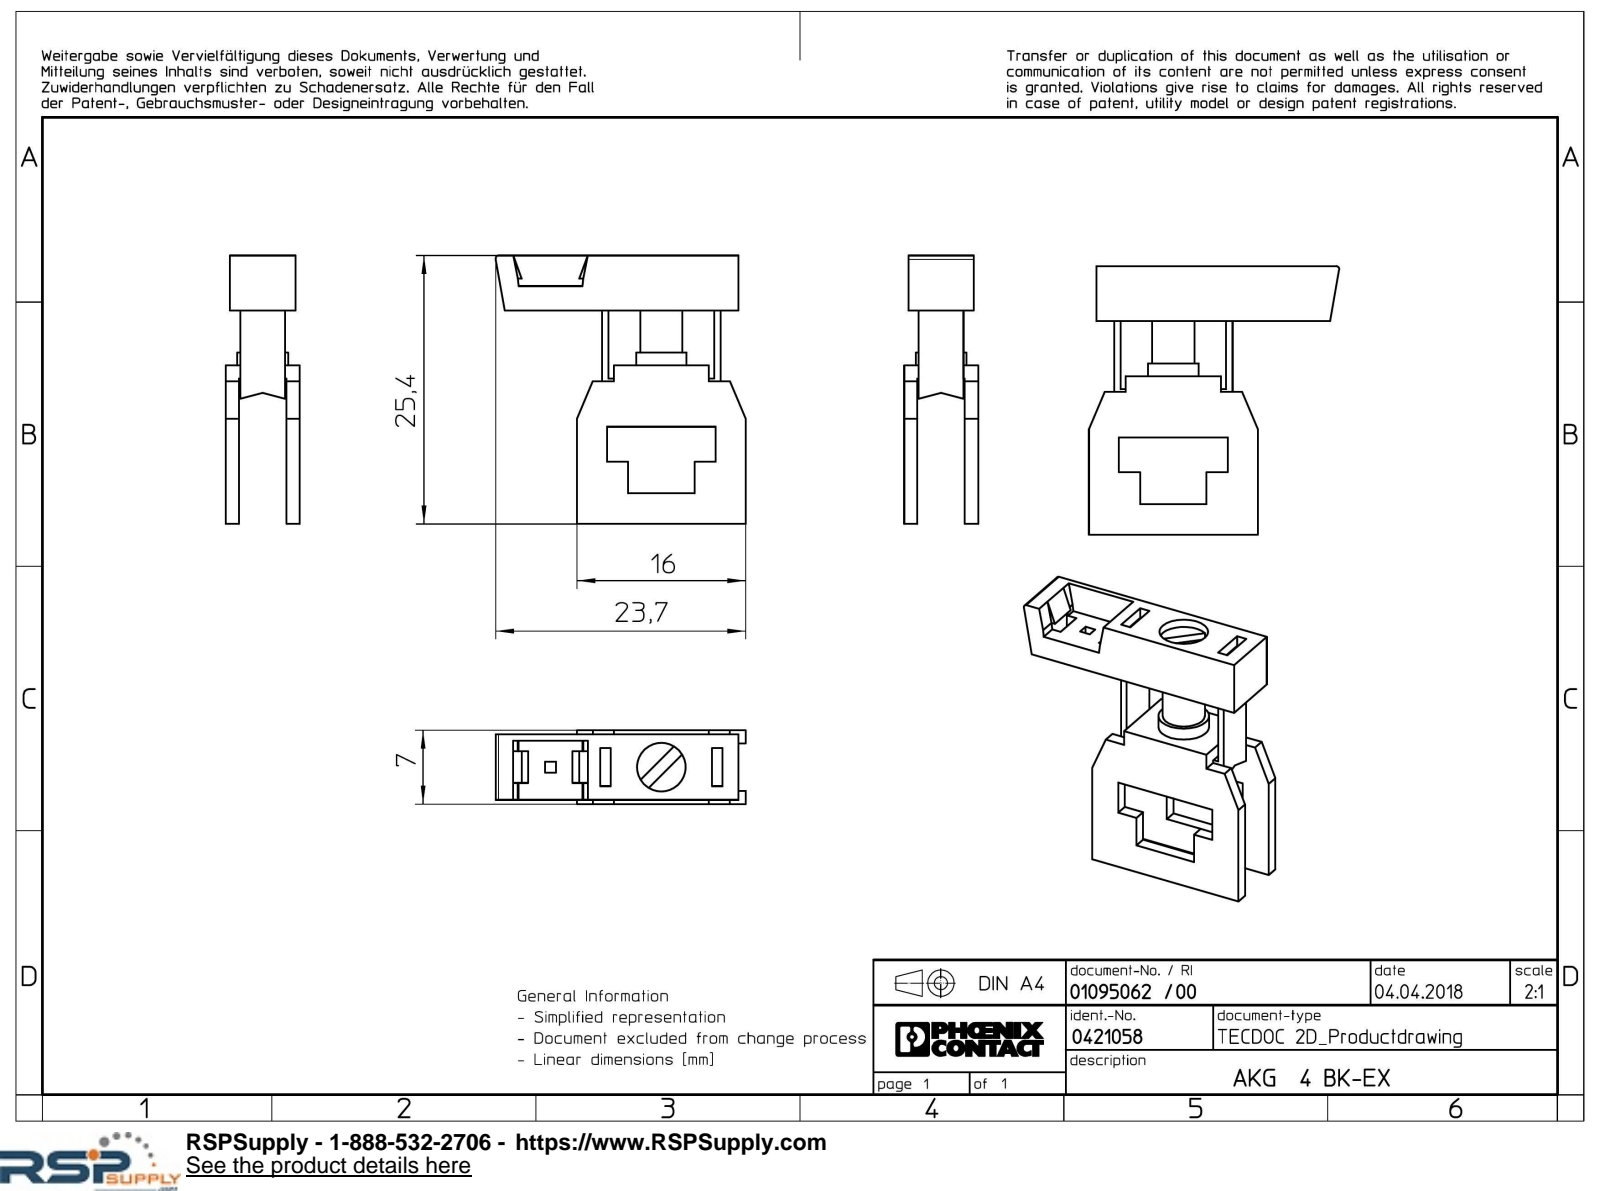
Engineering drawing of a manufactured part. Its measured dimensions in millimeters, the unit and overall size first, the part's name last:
Units: millimetres
Overall size (bounding box): 25.4 × 23.7 × 7
Round holes (diameter × count): ⌀4.6 ×1
Round bosses / shafts (diameter × count): ⌀4.8 ×1, ⌀4 ×1
Partial cylindrical surfaces — rounded edges, fillets, slot ends (radius × count): R0.3 ×1
Main face-to-face distances: 1.25, 5.75, 0.4, 6.6, 0.85, 5.35, 7, 4.5, 5.2, 6.2
Volume: 1 242 mm³ · Surface area: 1 910 mm²
Bodies: 1 solid, 108 faces (101 planar, 7 cylindrical, 0 other)
Part name (STEP PRODUCT): AKG_4_BK_EX_select
STEP written by: Creo Elements/Direct Modeling 20.1A 29-Sep-2018 (C) Parametric Technology GmbH (AUTOMOTIVE_DESIGN)
